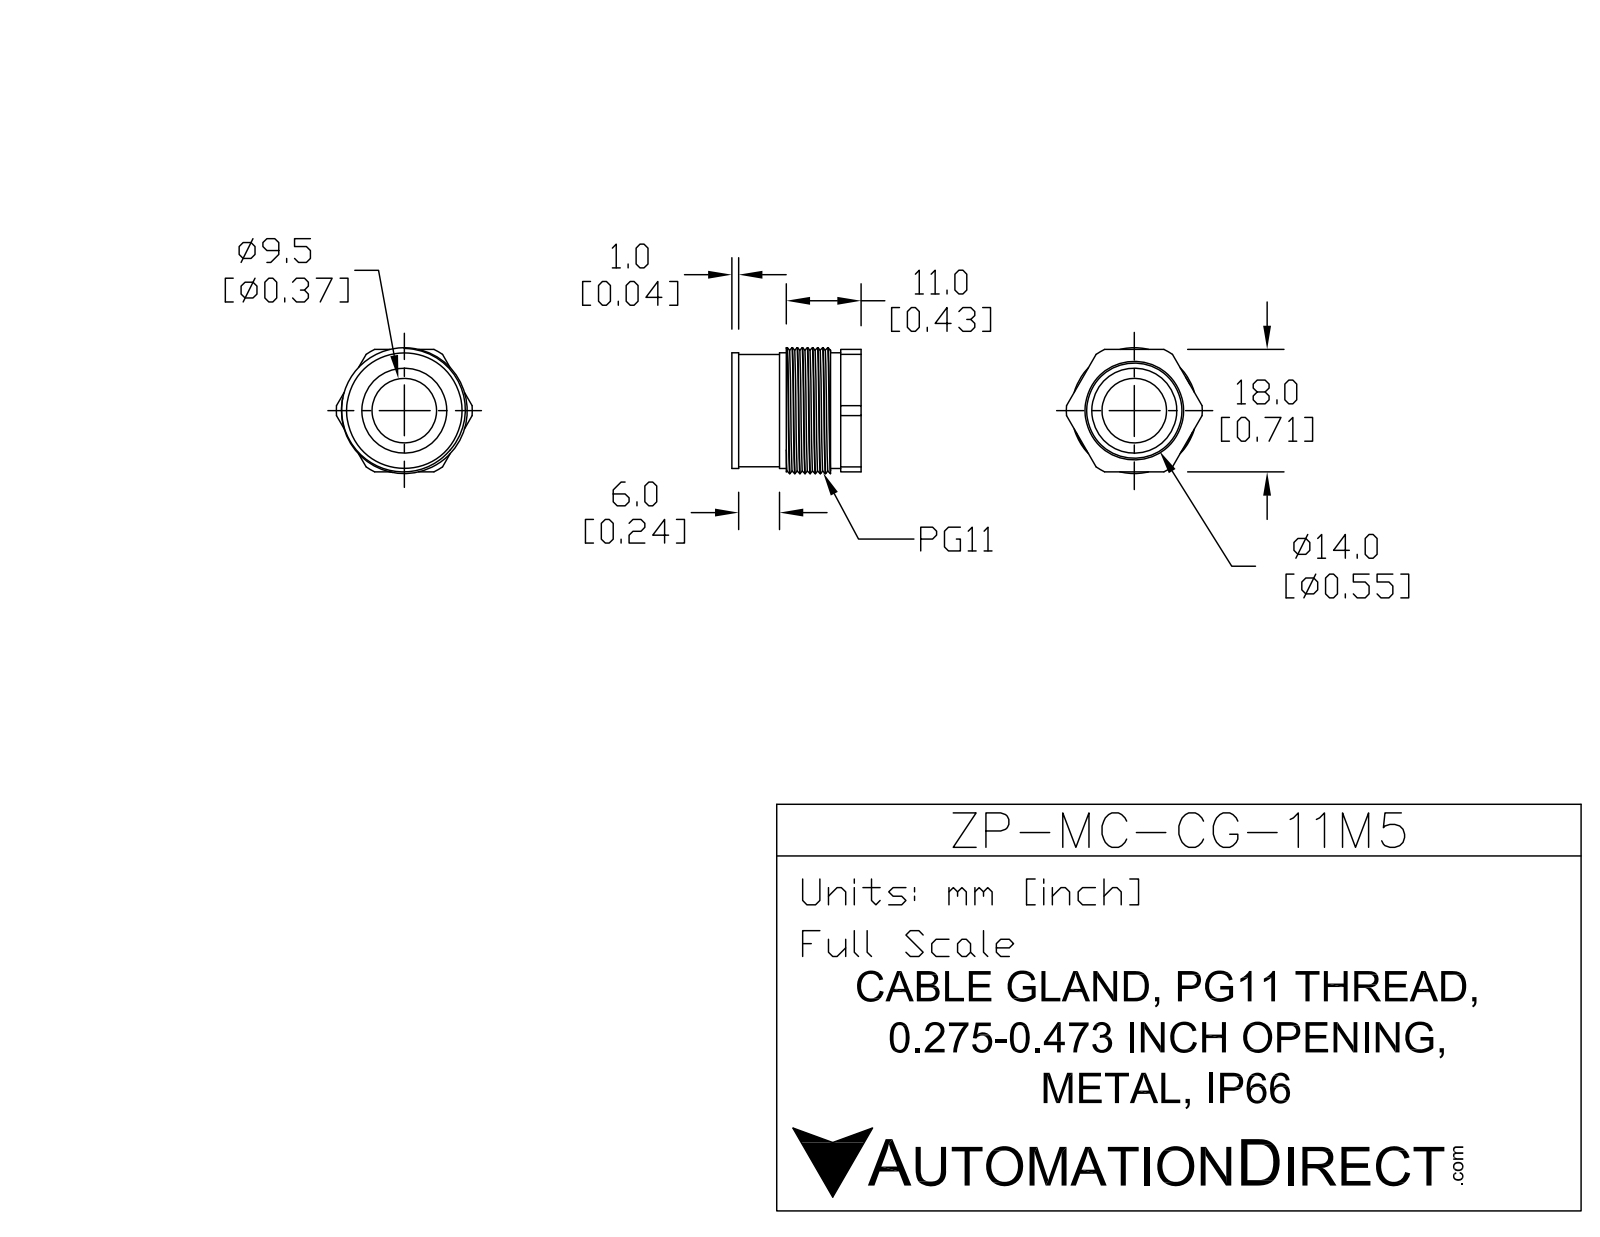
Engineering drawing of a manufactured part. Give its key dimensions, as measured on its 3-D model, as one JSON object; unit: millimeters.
{"part_name": "ZP-MC-CG-11M5", "step_written_by": "SolidWorks 2011 (AUTOMOTIVE_DESIGN)", "units": "millimeters", "bodies": {"solids": 1, "faces": 36, "planar": 17, "cylindrical": 15, "other": 4}, "overall_size": [20, 19, 18.5], "volume_mm3": 2192, "surface_area_mm2": 2453, "round_holes": [[9.5, 1], [12.5, 1], [14, 1]], "round_bosses_or_shafts": [[18.5, 1], [17, 1], [16.5, 1]], "partial_cylinders_radius": [[10, 1]], "face_to_face_distances": [18, 1, 7, 8, 19, 11, 12, 6, 3, 9]}
